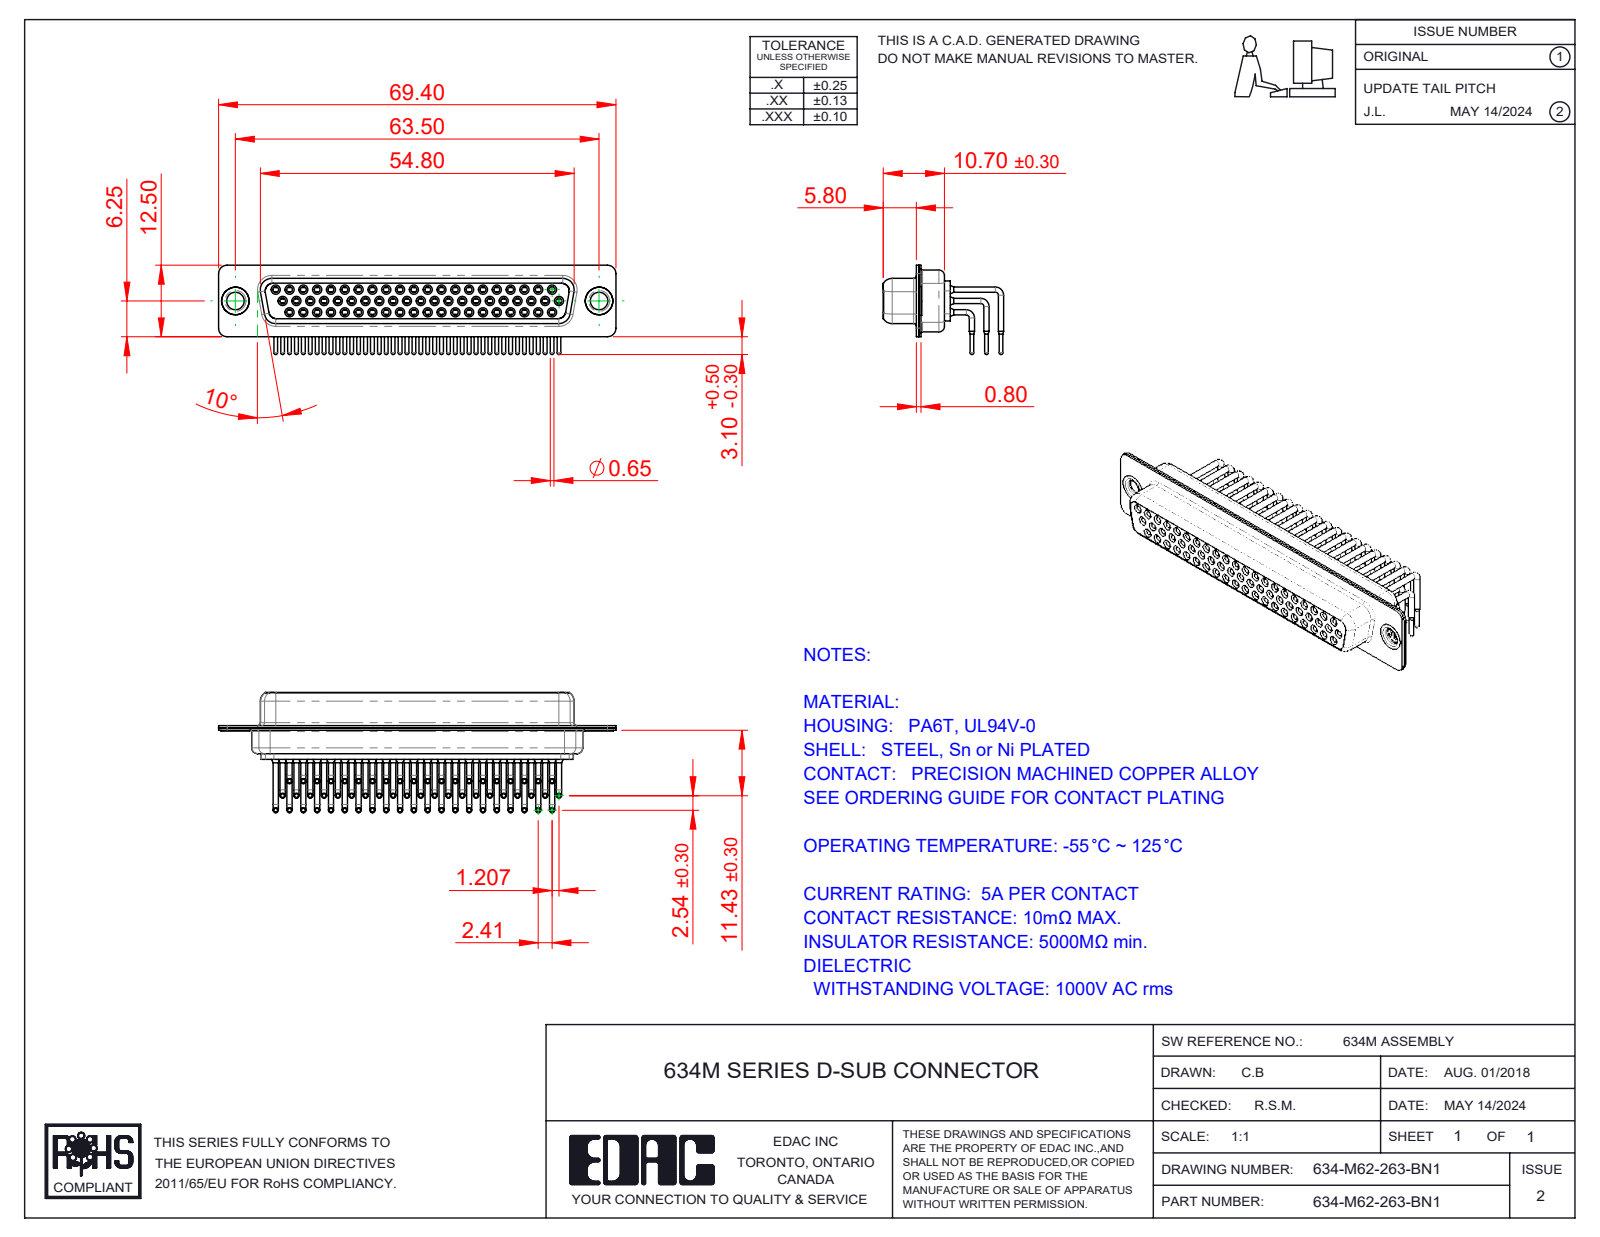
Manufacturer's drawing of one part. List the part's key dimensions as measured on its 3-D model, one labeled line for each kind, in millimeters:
Part name (STEP PRODUCT): 634M Contact Row 2; 634M Housing_62 Contacts; 634-M62-263-BN1; 634M Shell Rear_62 Contacts (+4 more)
STEP written by: SolidWorks 2016 (CONFIG_CONTROL_DESIGN)
Units: millimetres
Bodies: 67 solids, 3539 faces (997 planar, 1547 cylindrical, 995 other)
Overall size (bounding box): 69.4 × 21.02 × 15.6
Volume: 5 326 mm³ · Surface area: 17 717 mm²
Round holes (diameter × count): ⌀1 ×62, ⌀1.1 ×62, ⌀1.7 ×62, ⌀1.8 ×62, ⌀2 ×62, ⌀3.05 ×2, ⌀4 ×2, ⌀4.8 ×2
Round bosses / shafts (diameter × count): ⌀0.9 ×124, ⌀1.6 ×62, ⌀1.5 ×62, ⌀0.65 ×62, ⌀2 ×56, ⌀5 ×2, ⌀4.9 ×2, ⌀3.55 ×2
Partial cylindrical surfaces — rounded edges, fillets, slot ends (radius × count): R1.5 ×16, R2 ×12, R1.35 ×8, R1.6 ×8, R0.25 ×4, R0.5 ×4, R0.6 ×4, R0.65 ×4
Main face-to-face distances: 0.4, 1.45, 8.95, 1.9, 8.5, 2.3, 6.2, 0.45, 7.05, 0.85
Hole centre spacings: 7.24, 2.32, 2.41, 9.65, 4.13, 4.83, 16.89, 14.48
